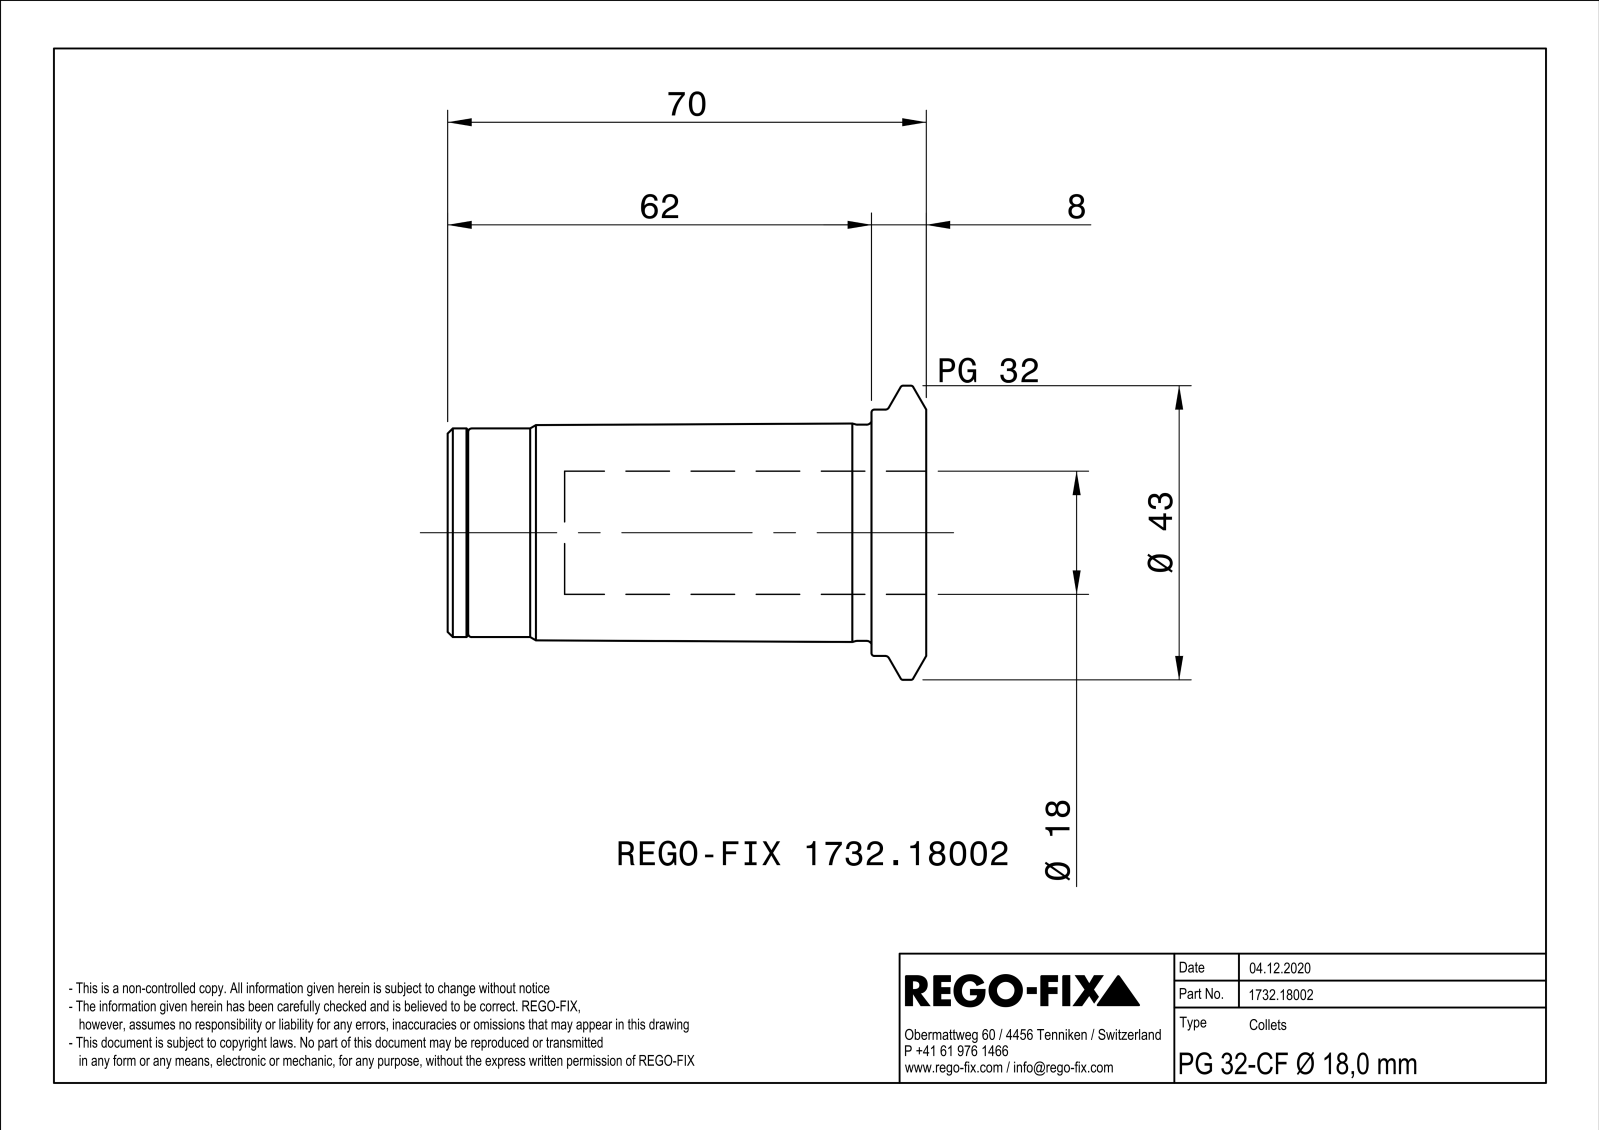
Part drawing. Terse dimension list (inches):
name: NOCUT
written by: SIEMENS PLM Software Solid Edge ST10 (AUTOMOTIVE_DESIGN)
unit: in
bodies: 1 solid, 130 faces (31 planar, 45 cylindrical, 54 other)
size: 2.756 × 1.693 × 1.693
volume: 2.37 in³; area: 25.97 in²
holes: 3× ⌀0.157, 1× ⌀0.351, 1× ⌀0.413, 1× ⌀0.709, 1× ⌀1.06, 1× ⌀1.122
bosses: 1× ⌀1.693, 1× ⌀1.417, 1× ⌀1.244, 1× ⌀1.201, 1× ⌀1.043, 1× ⌀0.827
rounds: 6× R0.079, 3× R0.039, 3× R0.138, 1× R0.157, 1× R0.187, 1× R0.344
face distances: 0.039, 2.756, 2.283, 0.472, 2.323, 0.433, 0.315, 2.362, 0.079, 0.394
hole spacings: 0.305, 0.528, 0.529
